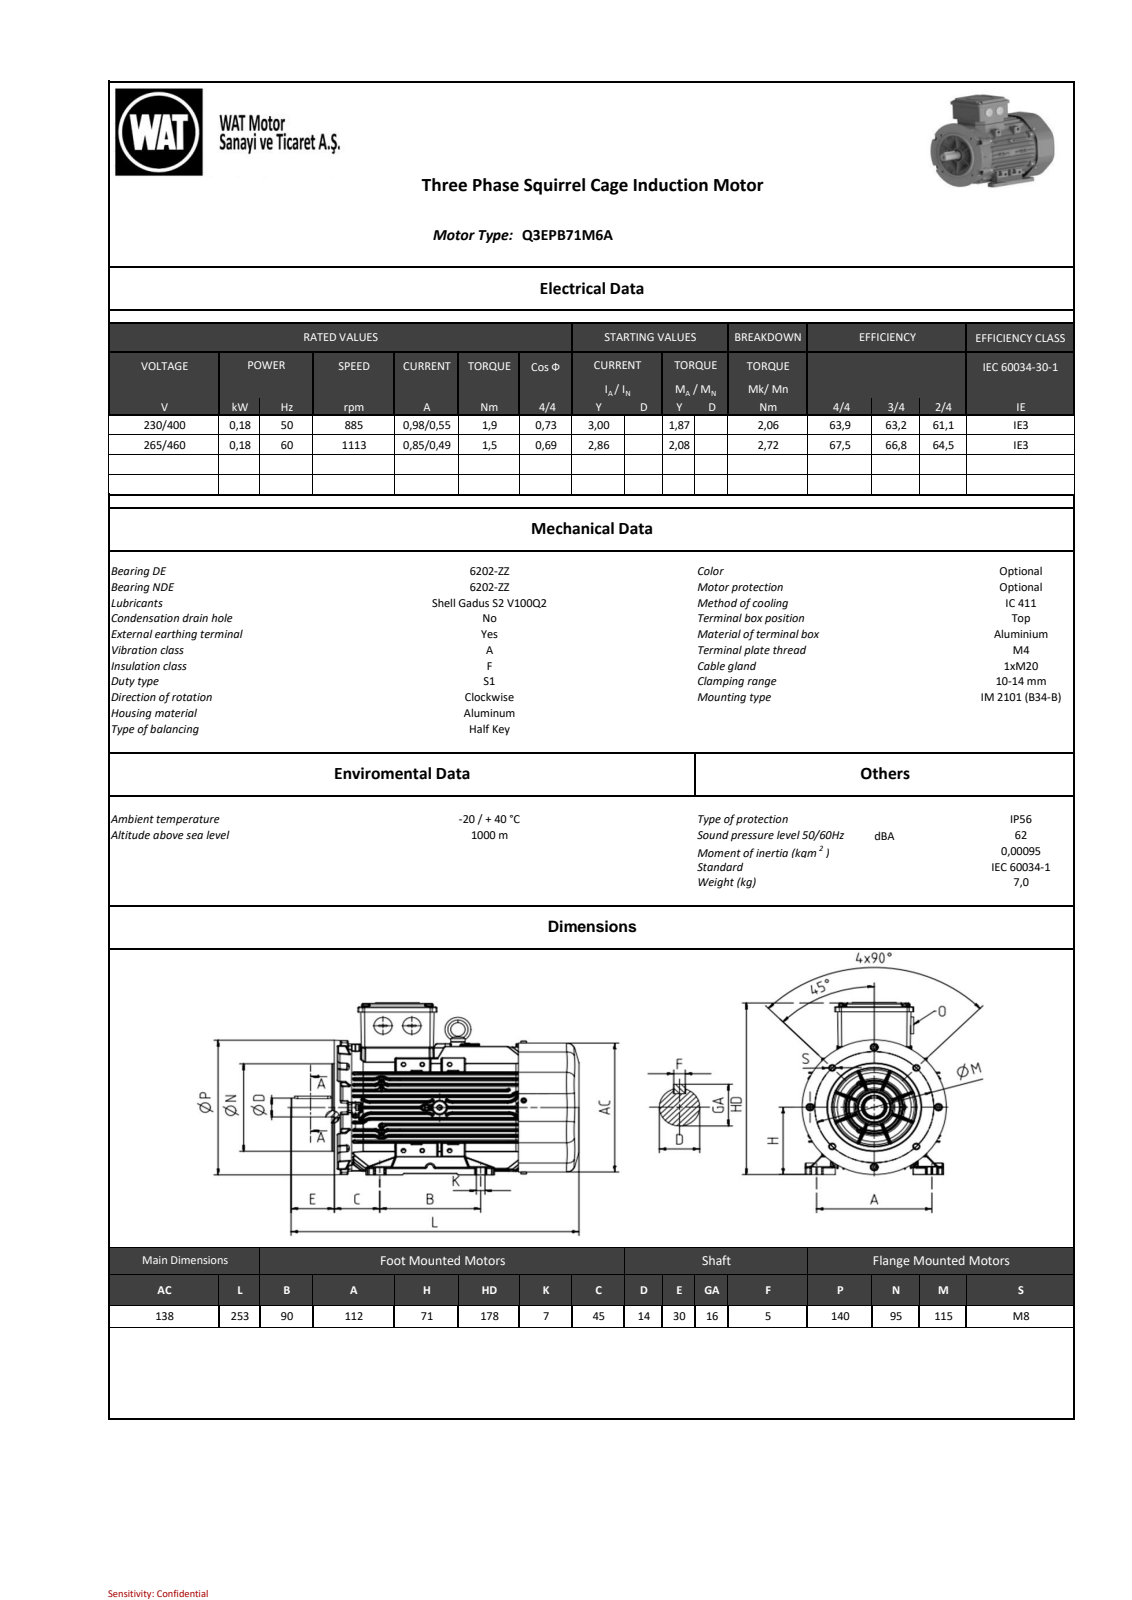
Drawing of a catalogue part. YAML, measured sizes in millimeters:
part_name: "001_objects"
step_written_by: "SIEMENS PLM Software NX2206.8101 (AUTOMOTIVE_DESIGN)"
units: millimeters
bodies: {solids: 0, faces: 2854, planar: 1424, cylindrical: 745, other: 685}
overall_size: [252, 178.11, 140.48]
round_holes:
  - {diameter: 3.3, count: 9}
  - {diameter: 3.65, count: 8}
  - {diameter: 2.5, count: 6}
  - {diameter: 5, count: 5}
  - {diameter: 8, count: 5}
  - {diameter: 4, count: 4}
  - {diameter: 4.5, count: 4}
  - {diameter: 4.65, count: 4}
  - {diameter: 4.8, count: 4}
  - {diameter: 5.2, count: 4}
  - {diameter: 7, count: 4}
  - {diameter: 3, count: 3}
round_bosses_or_shafts:
  - {diameter: 8, count: 8}
  - {diameter: 4, count: 8}
  - {diameter: 3.3, count: 4}
  - {diameter: 140.48, count: 1}
  - {diameter: 138, count: 1}
  - {diameter: 136, count: 1}
  - {diameter: 115, count: 1}
  - {diameter: 95, count: 1}
partial_cylinders:
  - {radius: 1, count: 95}
  - {radius: 0.5, count: 54}
  - {radius: 2, count: 43}
  - {radius: 1.2, count: 36}
  - {radius: 1.5, count: 28}
  - {radius: 4, count: 17}
  - {radius: 0.1, count: 14}
  - {radius: 2.5, count: 14}
face_to_face_distances: [2, 3, 1, 185.5, 35, 4, 5, 15, 83, 6.9]
hole_center_spacings: [61.39, 84.47, 55, 36.59, 67.18, 67.2, 92.35, 60]
